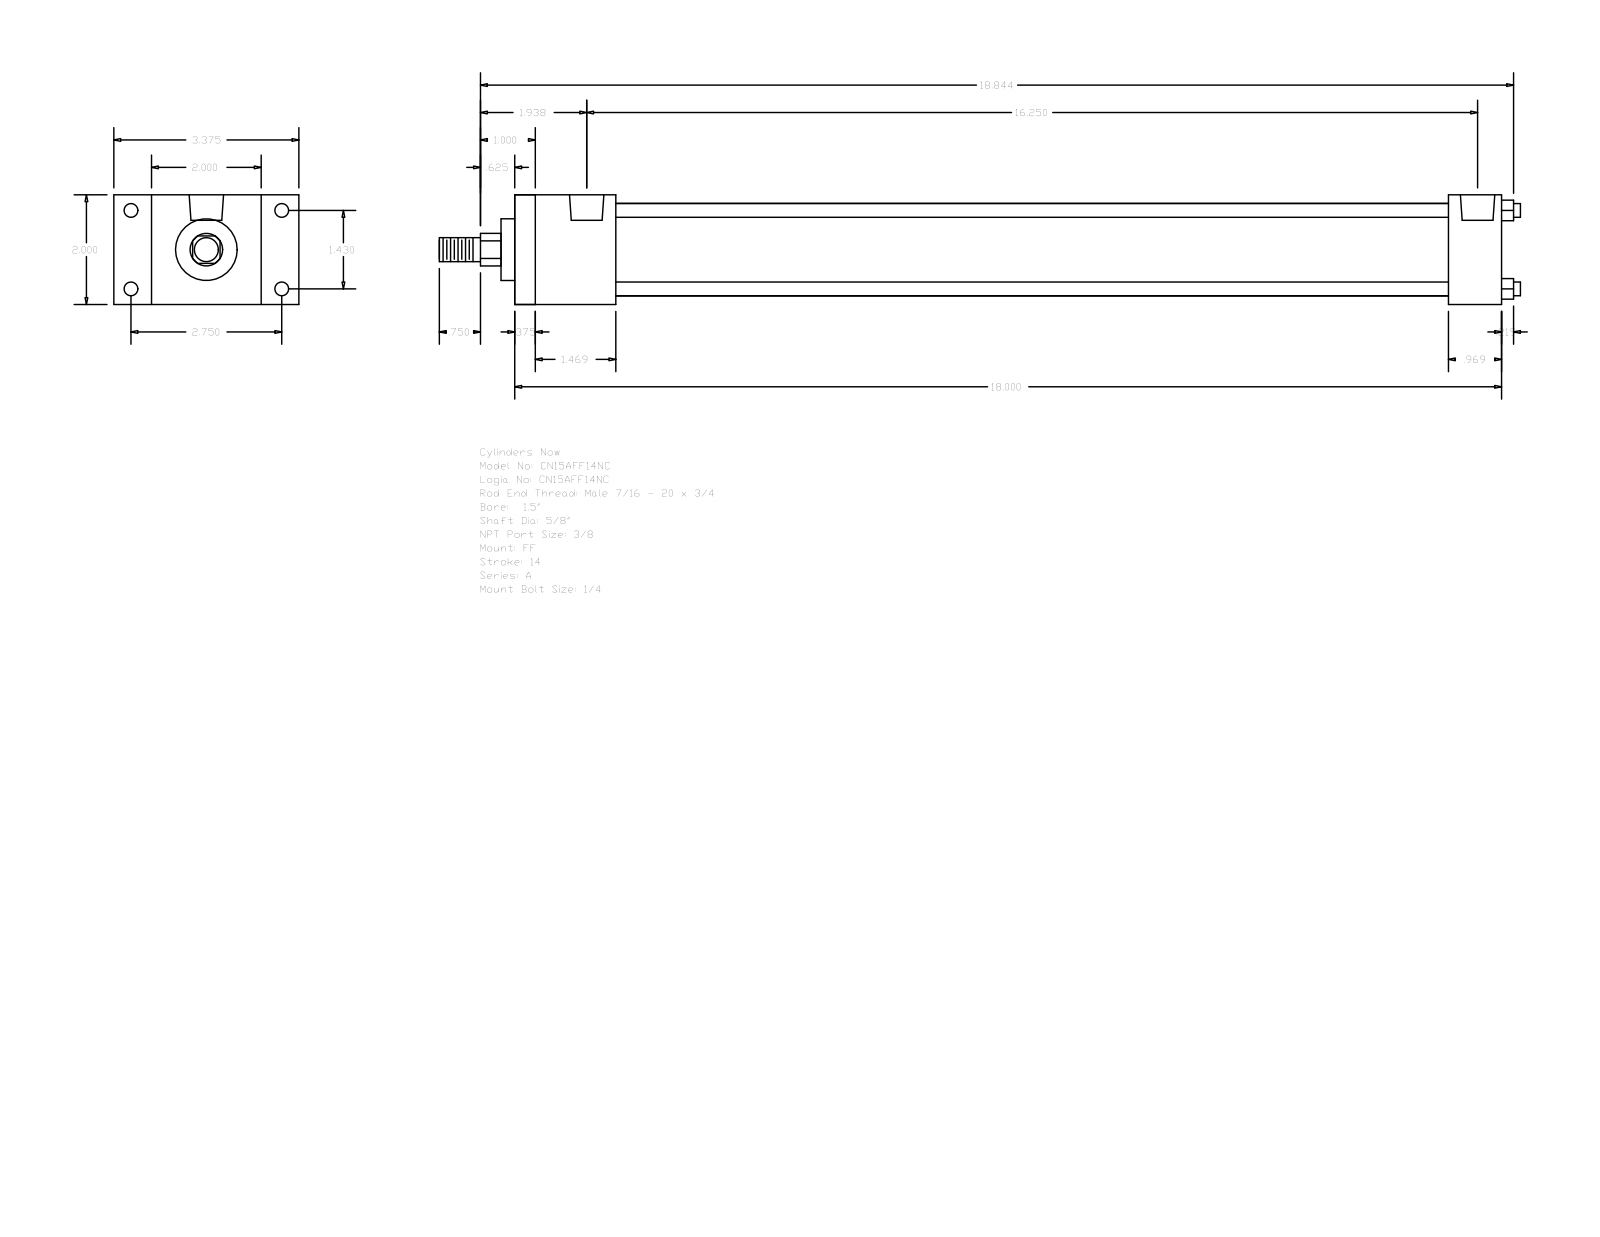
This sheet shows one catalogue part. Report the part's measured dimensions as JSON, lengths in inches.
{"part_name": "A_FF__0150_0.625", "step_written_by": "GSSL Pune (CONFIG_CONTROL_DESIGN)", "units": "inches", "bodies": {"solids": 0, "faces": 92, "planar": 64, "cylindrical": 28, "other": 0}, "overall_size": [19.719, 3.375, 2], "round_holes": [[0.219, 4], [0.25, 4], [0.627, 2]], "round_bosses_or_shafts": [[0.25, 4], [1.69, 1], [1.125, 1], [0.625, 1], [0.437, 1]], "partial_cylinders_radius": [[0.297, 1]], "face_to_face_distances": [2, 18, 0.375, 17.625, 1.844, 17.031, 1.469, 16.656, 15.187, 16.156], "hole_center_spacings": [0.156, 1.43, 2.75, 3.099, 15.937, 16.094, 16.25]}
